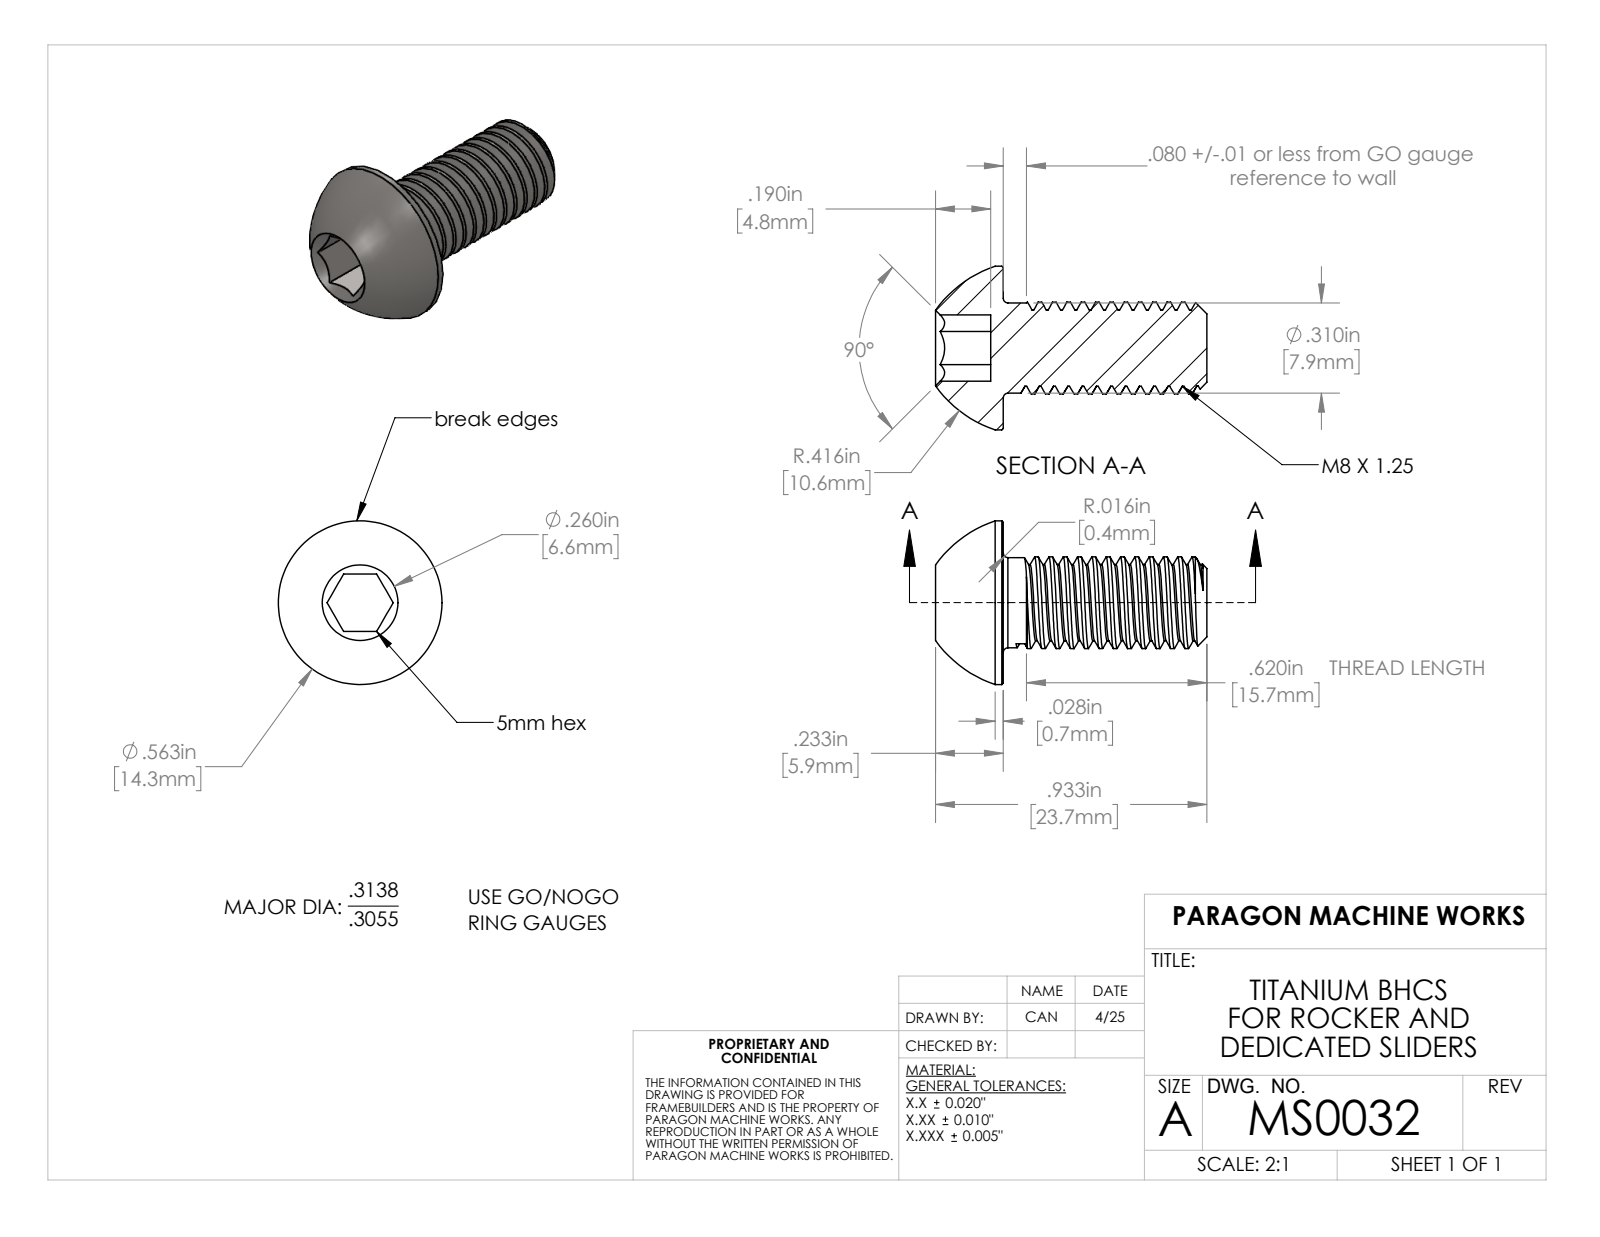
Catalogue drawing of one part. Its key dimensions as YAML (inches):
part_name: "MS0032"
step_written_by: "SolidWorks 2023 (AUTOMOTIVE_DESIGN)"
units: inches
bodies: {solids: 1, faces: 53, planar: 10, cylindrical: 29, other: 14}
overall_size: [0.933, 0.562, 0.562]
volume: 0.081
surface_area: 1.778
round_bosses_or_shafts:
  - {diameter: 0.563, count: 1}
  - {diameter: 0.315, count: 1}
  - {diameter: 0.31, count: 1}
face_to_face_distances: [0.197, 0.7, 0.043, 0.743]
